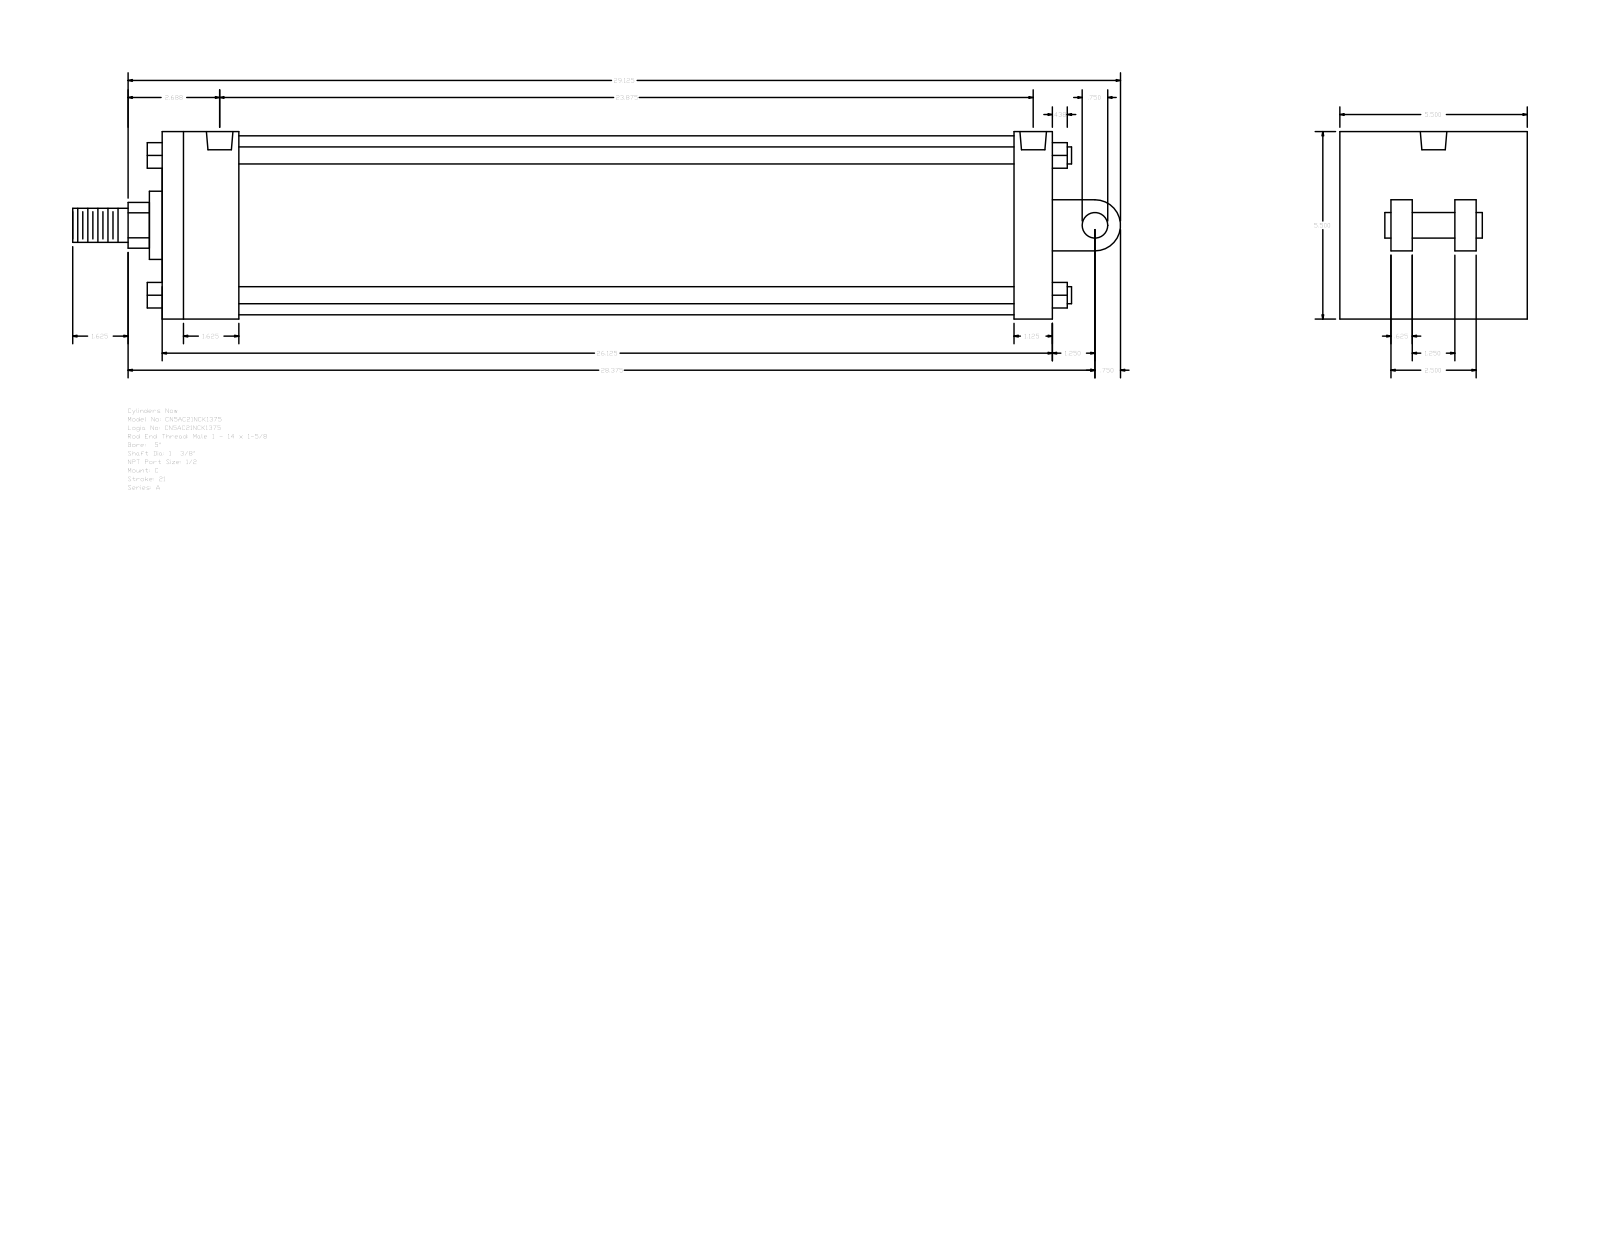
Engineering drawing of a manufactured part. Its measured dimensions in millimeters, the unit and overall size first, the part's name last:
Units: millimetres
Overall size (bounding box): 781.05 × 139.7 × 139.7
Round holes (diameter × count): ⌀8.73 ×4, ⌀19.77 ×2
Round bosses / shafts (diameter × count): ⌀12.7 ×4, ⌀133.35 ×1, ⌀50.8 ×1, ⌀34.92 ×1, ⌀25.4 ×1, ⌀19.05 ×1
Partial cylindrical surfaces — rounded edges, fillets, slot ends (radius × count): R17.06 ×1, R19.05 ×1
Main face-to-face distances: 139.7, 663.58, 57.15, 28.58, 635, 577.85, 606.43, 38.1, 53.97, 85.73
Hole centre spacings: 2.39, 601.65, 604.04, 606.43
Bodies: 0 solids, 135 faces (102 planar, 33 cylindrical, 0 other)
Part name (STEP PRODUCT): A_C__0500_1.375
STEP written by: GSSL Pune (CONFIG_CONTROL_DESIGN)
